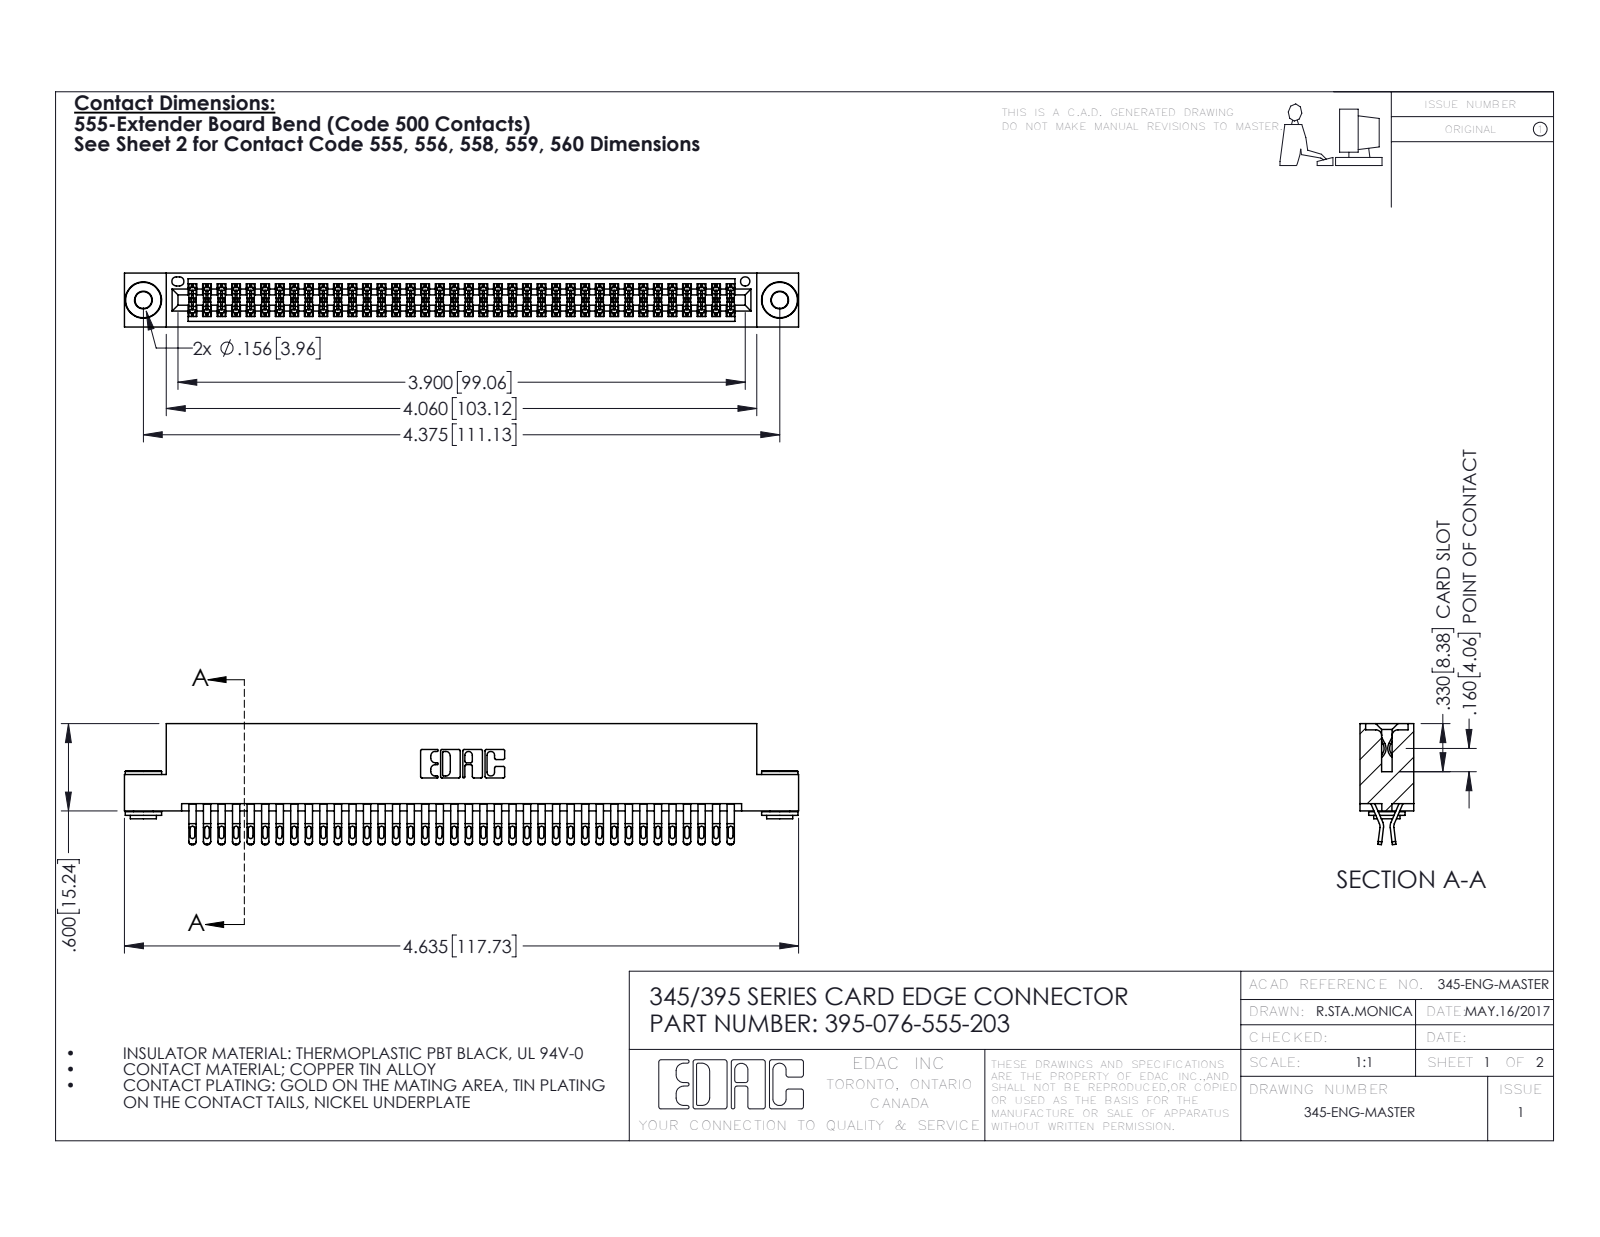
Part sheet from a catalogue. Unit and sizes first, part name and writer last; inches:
Units: inches
Overall size (bounding box): 4.635 × 0.832 × 0.37
Round holes (diameter × count): ⌀0.116 ×2, ⌀0.156 ×2, ⌀0.064 ×1
Round bosses / shafts (diameter × count): ⌀0.25 ×2, ⌀0.18 ×2, ⌀0.136 ×2
Partial cylindrical surfaces — rounded edges, fillets, slot ends (radius × count): R0.016 ×190, R0.02 ×152, R0.006 ×114, R0.01 ×22, R0.007 ×6, R0.031 ×6, R0.026 ×3, R0.01 ×2
Main face-to-face distances: 0.072, 0.298, 0.2, 0.025, 0.37, 0.098, 0.272, 0.225, 0.175, 0.149
Hole centre spacings: 0.27, 4.139, 4.375
Volume: 0.71 in³ · Surface area: 28.05 in²
Bodies: 79 solids, 4420 faces (2446 planar, 1966 cylindrical, 8 other)
Part name (STEP PRODUCT): 345-292-001_555 Tail; 395-076-555-203; 345-250-002_345-250-002-102; 345 Part_Flush Mounting Lugs - 0.156 Dia-TH
STEP written by: SolidWorks 2016 (CONFIG_CONTROL_DESIGN)
